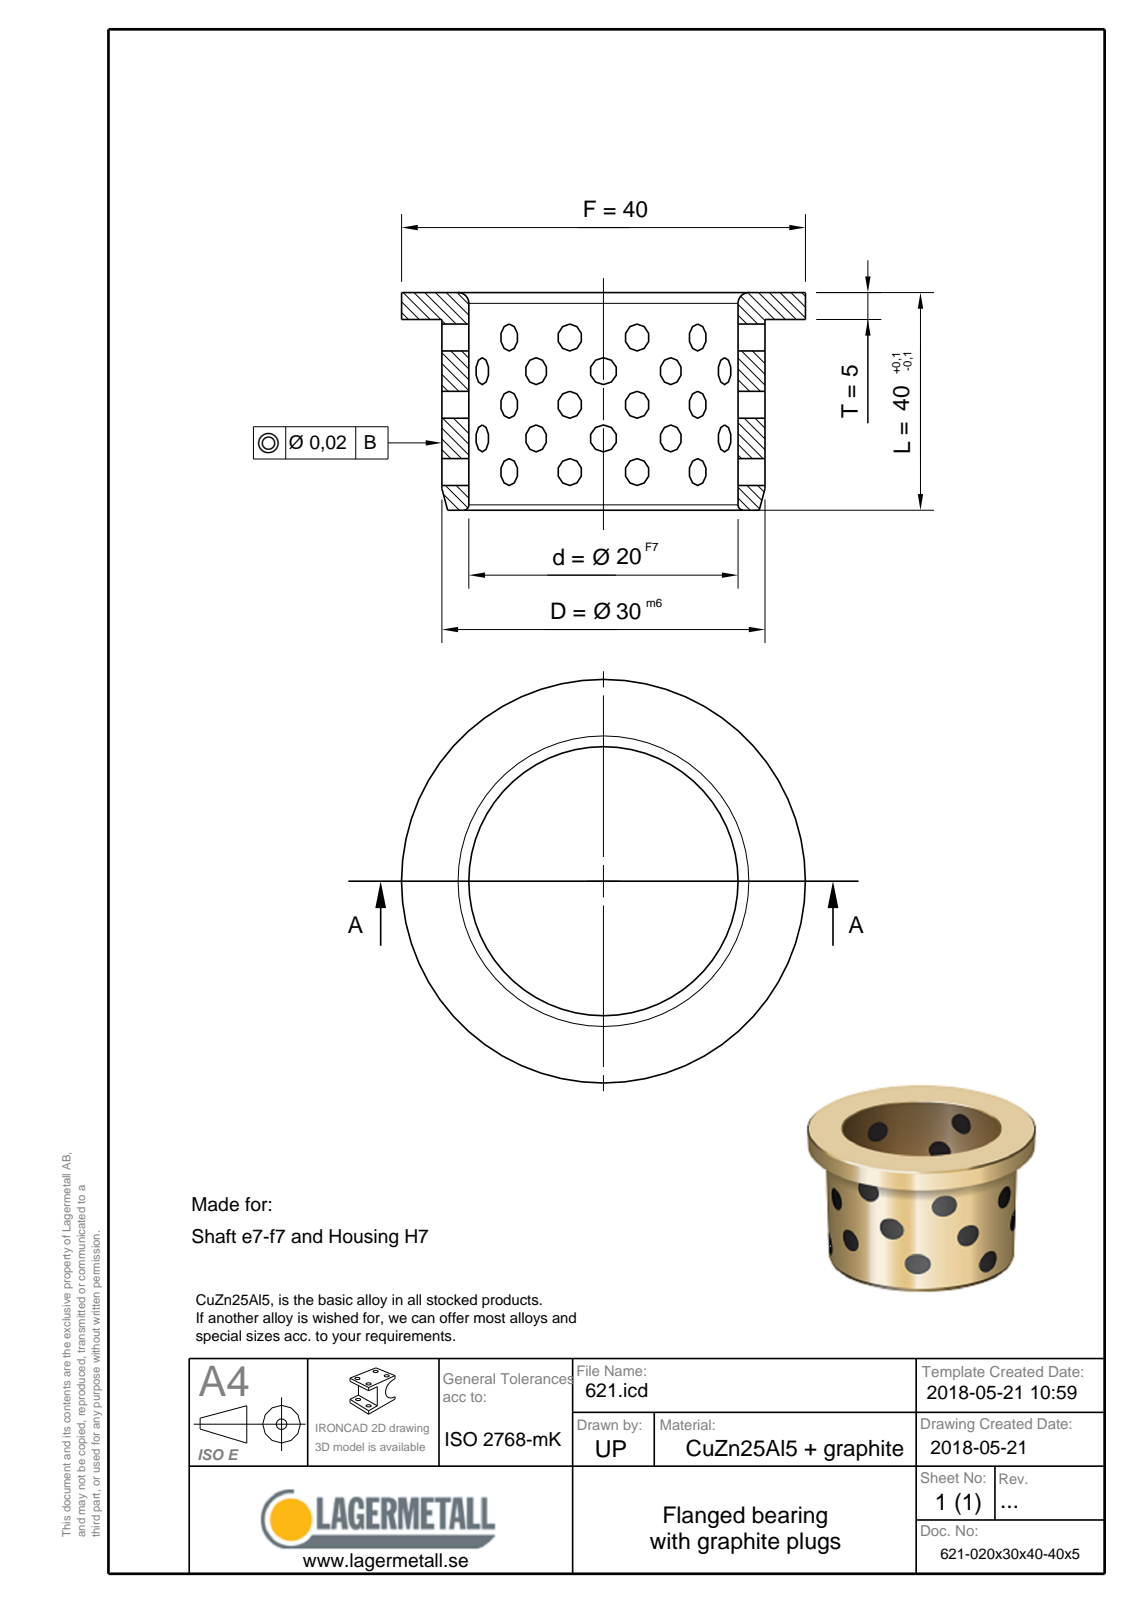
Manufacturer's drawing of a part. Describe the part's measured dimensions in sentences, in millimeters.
The part is named "621-020x30x40-40x5". Its 3-D file was written by "Spatial InterOp 3D (CONFIG_CONTROL_DESIGN)". It is 1 solid with 9 faces: 3 planar, 3 cylindrical and 3 other. Overall it measures 40 by 40 by 40 millimeters. Its volume is 18 325 cubic millimeters and its surface area 8 184 square millimeters. Round holes: 1 of diameter 20. Round bosses or shafts: 1 of diameter 40, 1 of diameter 30. The main face-to-face distances are 5, 35, 40.
